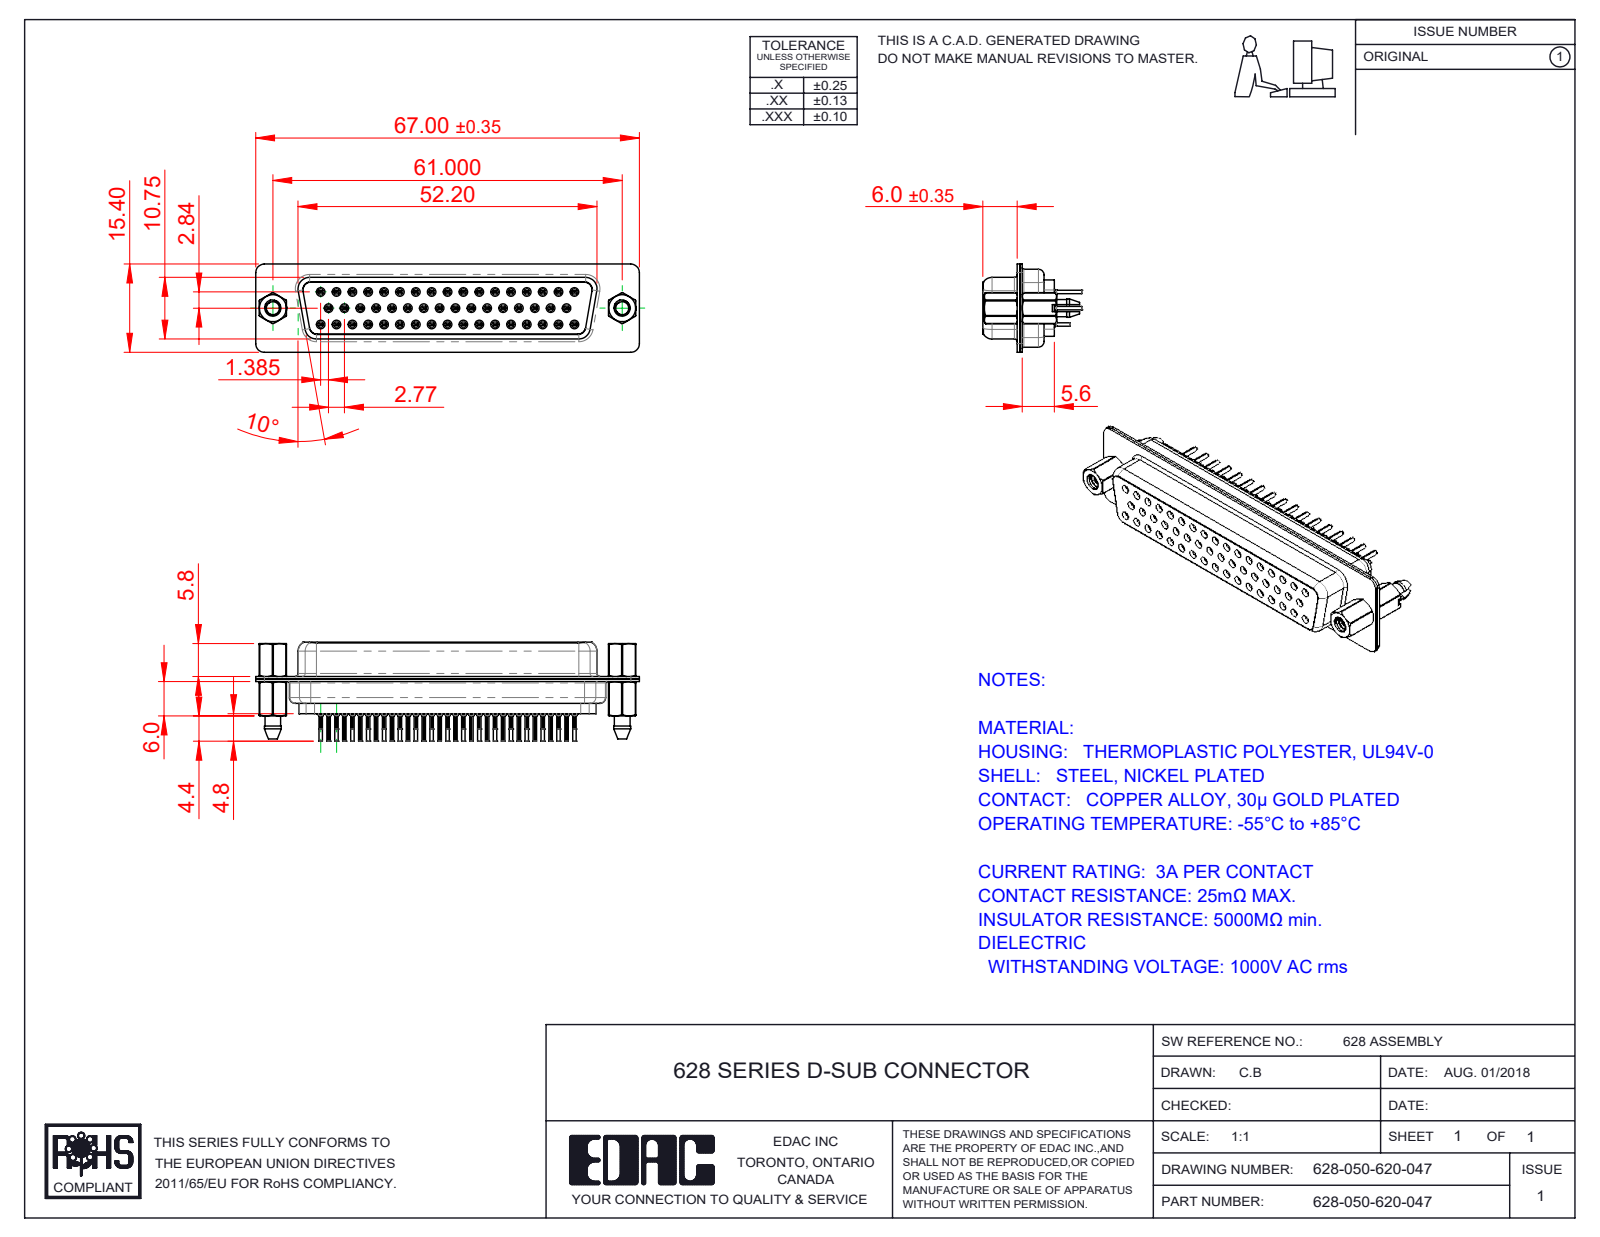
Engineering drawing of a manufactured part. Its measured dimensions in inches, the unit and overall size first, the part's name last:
Units: inches
Overall size (bounding box): 2.638 × 0.681 × 0.606
Round holes (diameter × count): ⌀0.008 ×50, ⌀0.031 ×50, ⌀0.035 ×50, ⌀0.043 ×50, ⌀0.063 ×50, ⌀0.067 ×17, ⌀0.089 ×2, ⌀0.09 ×2, ⌀0.157 ×2, ⌀0.159 ×2, ⌀0.191 ×2
Round bosses / shafts (diameter × count): ⌀0.079 ×50, ⌀0.059 ×50, ⌀0.047 ×50, ⌀0.024 ×50, ⌀0.195 ×2, ⌀0.189 ×2, ⌀0.11 ×2
Partial cylindrical surfaces — rounded edges, fillets, slot ends (radius × count): R0.004 ×100, R0.011 ×33, R0.059 ×18, R0.079 ×12, R0.053 ×8, R0.063 ×6, R0.01 ×4, R0.02 ×4
Main face-to-face distances: 0.018, 0.016, 0.446, 0.074, 0.406, 0.256, 0.035, 0.238, 0.236, 0.254
Hole centre spacings: 0.124, 0.109, 0.218, 0.327, 0.436, 0.545, 0.654, 0.763
Volume: 0.43 in³ · Surface area: 24.88 in²
Bodies: 57 solids, 6829 faces (1671 planar, 1891 cylindrical, 3267 other)
Part name (STEP PRODUCT): 628 Contact Row 1_20L; 628 Shell Front_50 Contacts; 628-050-620-047; 628 4-40 Hex Standoff (+5 more)
STEP written by: SolidWorks 2020 (CONFIG_CONTROL_DESIGN)
